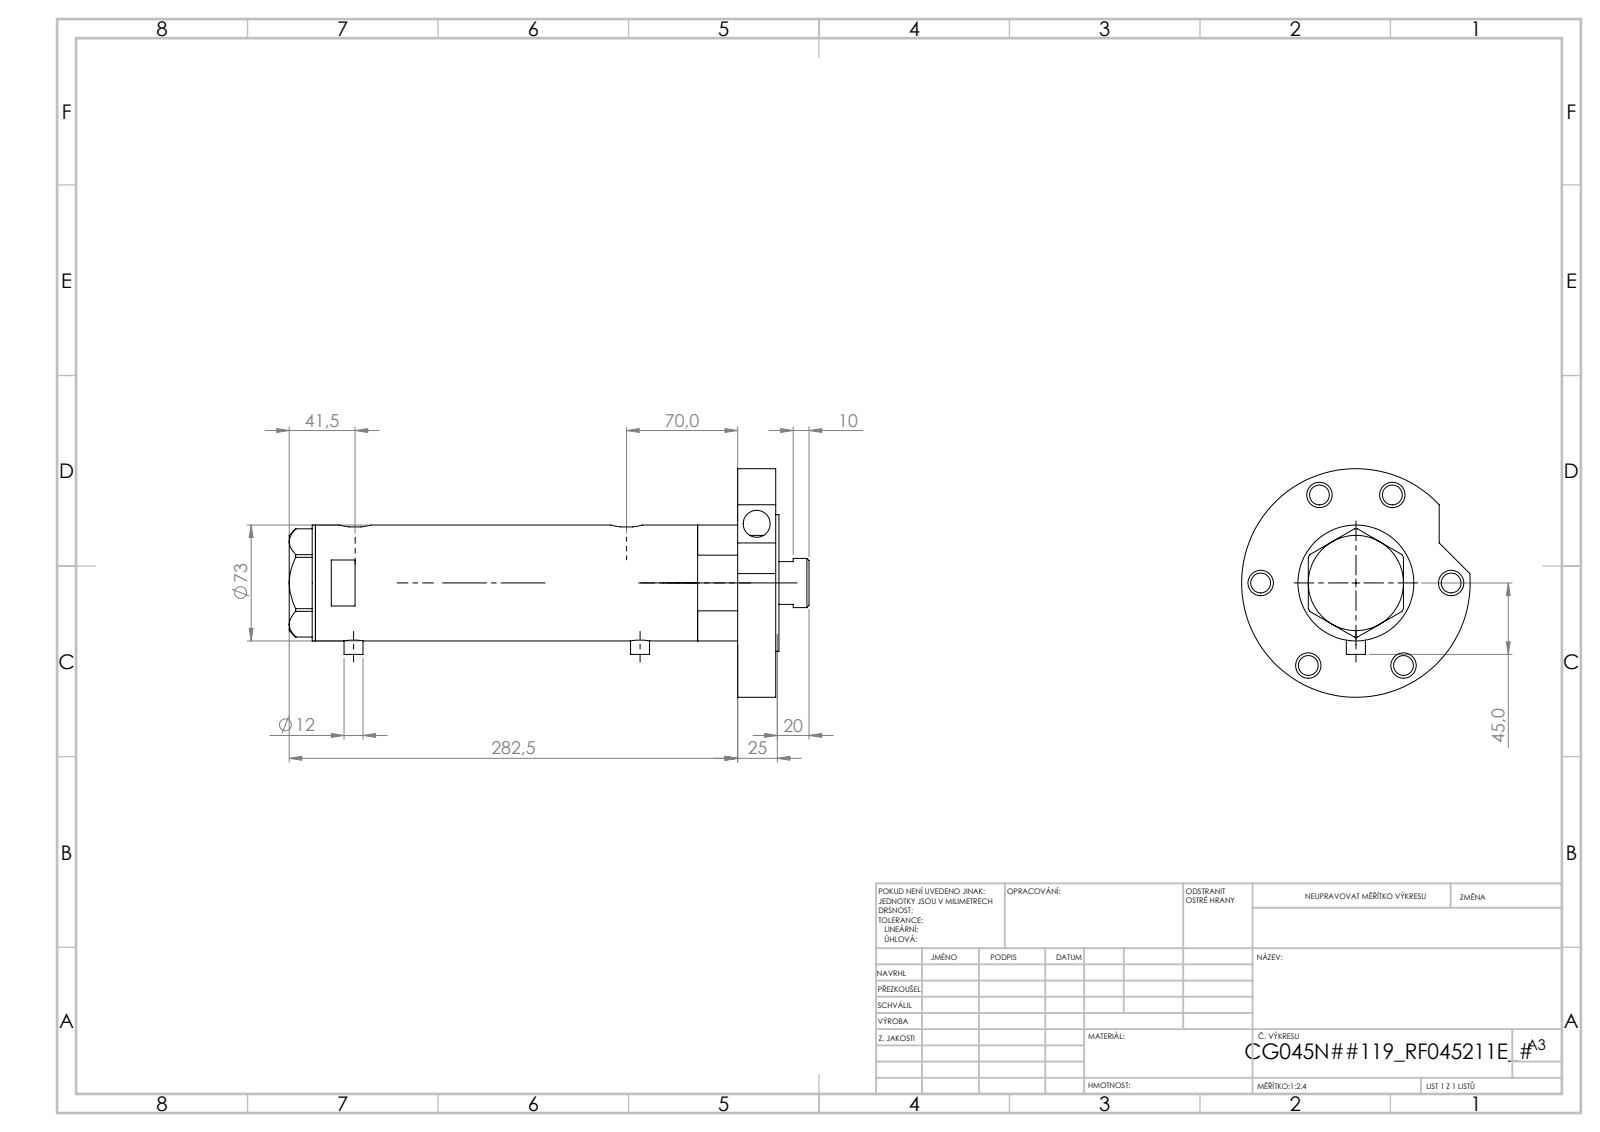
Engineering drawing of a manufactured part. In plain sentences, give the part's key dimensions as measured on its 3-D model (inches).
The part is named "V270CG_RF211E; V270CG_MIDDLE; V270CG_BACK; V270CG_FRONT (+1 more)". Its 3-D file was written by "SolidWorks 2019 (CONFIG_CONTROL_DESIGN)". It is 5 solids with 169 faces: 61 planar, 88 cylindrical and 20 other. Overall it measures 12.225 by 5.669 by 5.669 inches. Its volume is 82.08 cubic inches and its surface area 354.2 square inches. Round holes: 8 of diameter 0.492, 6 of diameter 0.63, 2 of diameter 0.197, 2 of diameter 0.518, 1 of diameter 0.413, 1 of diameter 0.669, 1 of diameter 1.26, 1 of diameter 1.319, 1 of diameter 1.772, 1 of diameter 1.89, 1 of diameter 2.362, 1 of diameter 2.52. Round bosses or shafts: 2 of diameter 0.472, 1 of diameter 5.669, 1 of diameter 3.386, 1 of diameter 2.874, 1 of diameter 2.283, 1 of diameter 1.22. Partial cylindrical surfaces (rounded edges, fillets, slot ends): 2 of radius 0.394. The main face-to-face distances are 0.945, 9.702, 1.024, 10.647, 0.079, 10.726, 7.328, 2.374, 3.319, 6.305. The hole center spacings are 2.362, 2.625, 3.928, 4.091, 4.237, 4.714, 6.719, 0.039.
